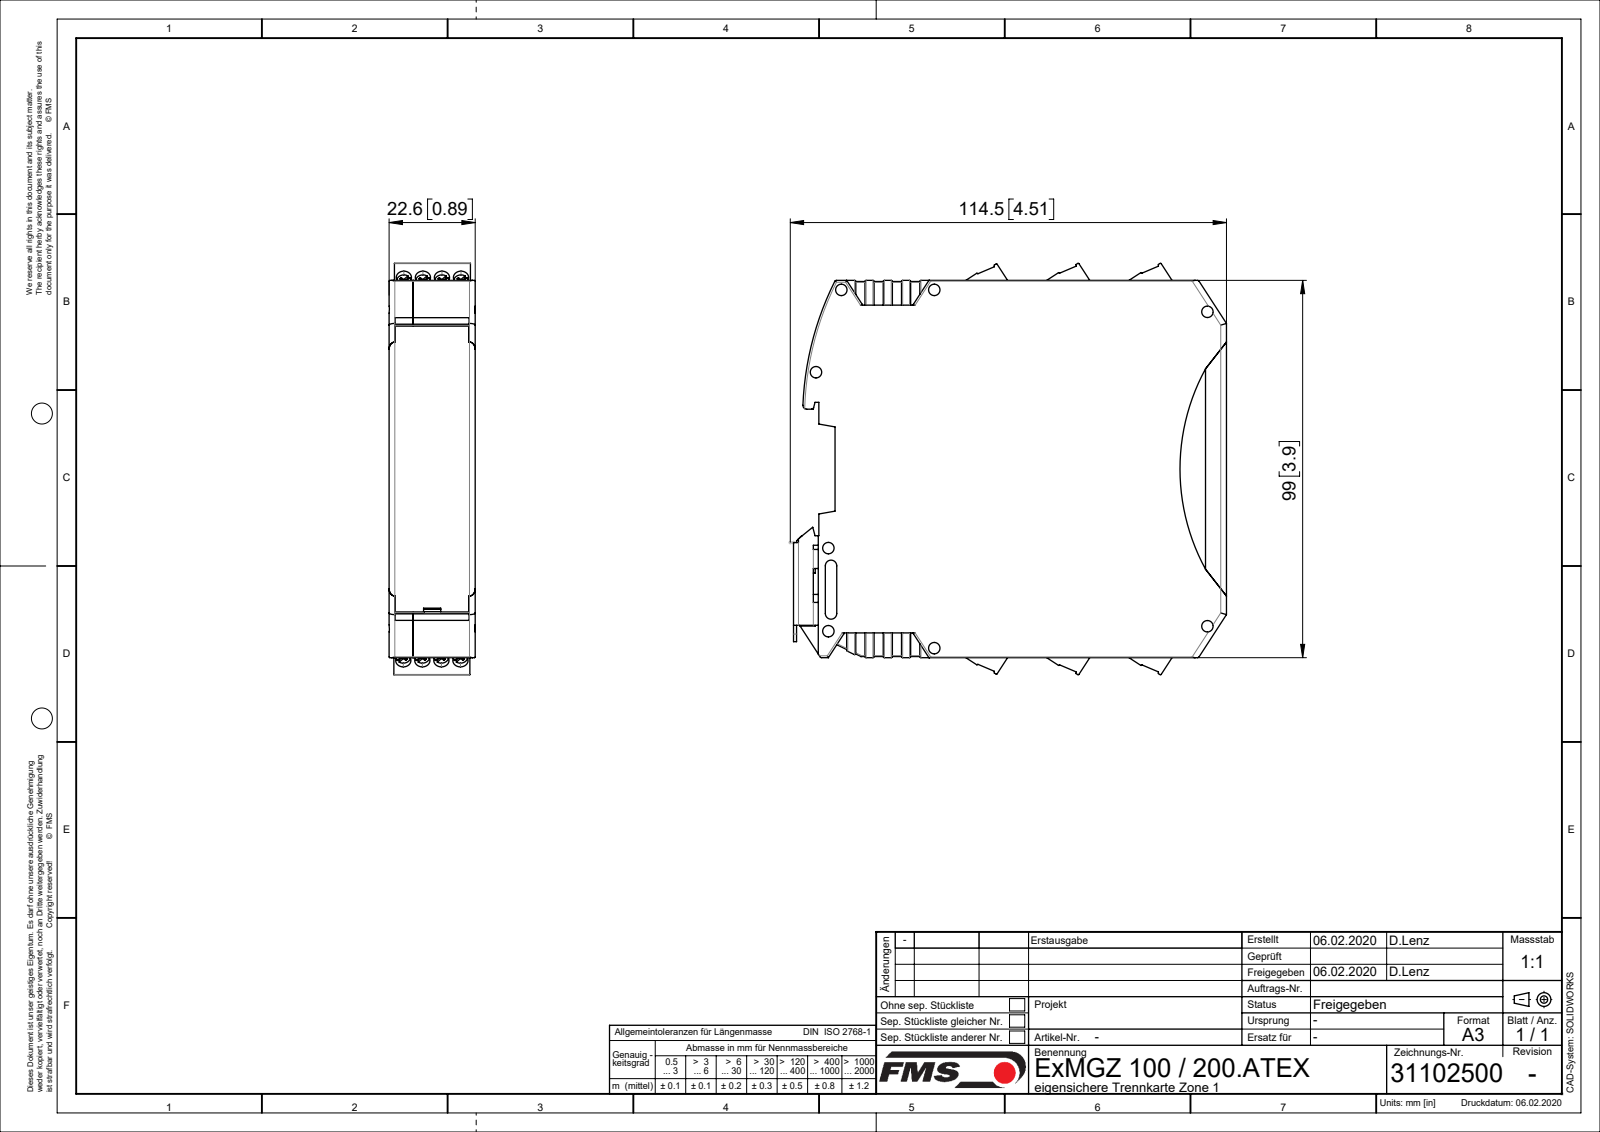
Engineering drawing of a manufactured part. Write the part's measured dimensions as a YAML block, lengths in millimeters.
part_name: "31102498_01; 31102500; 31102499_01"
step_written_by: "SolidWorks 2018 (CONFIG_CONTROL_DESIGN)"
units: millimeters
bodies: {solids: 12, faces: 3486, planar: 2507, cylindrical: 930, other: 49}
overall_size: [113.65, 107.96, 22.6]
volume: 58542
surface_area: 84554
round_holes:
  - {diameter: 1.4, count: 26}
  - {diameter: 2.8, count: 24}
  - {diameter: 4, count: 24}
  - {diameter: 3, count: 13}
  - {diameter: 1.5, count: 10}
  - {diameter: 2.9, count: 8}
  - {diameter: 1.6, count: 1}
  - {diameter: 3.2, count: 1}
round_bosses_or_shafts:
  - {diameter: 3.8, count: 24}
  - {diameter: 2.2, count: 6}
  - {diameter: 6, count: 1}
  - {diameter: 4.5, count: 1}
  - {diameter: 2.8, count: 1}
  - {diameter: 1.35, count: 1}
partial_cylinders:
  - {radius: 0.3, count: 101}
  - {radius: 0.5, count: 50}
  - {radius: 0.2, count: 24}
  - {radius: 0.8, count: 24}
  - {radius: 2.9, count: 24}
  - {radius: 1.5, count: 22}
  - {radius: 0.75, count: 18}
  - {radius: 2.5, count: 8}
face_to_face_distances: [1.25, 21.35, 22.6, 20.1, 1.2, 1, 2.55, 0.75, 18.12, 3.55]
hole_center_spacings: [5, 10, 12.77, 18.8, 15, 11.75, 15.43, 18.13]
